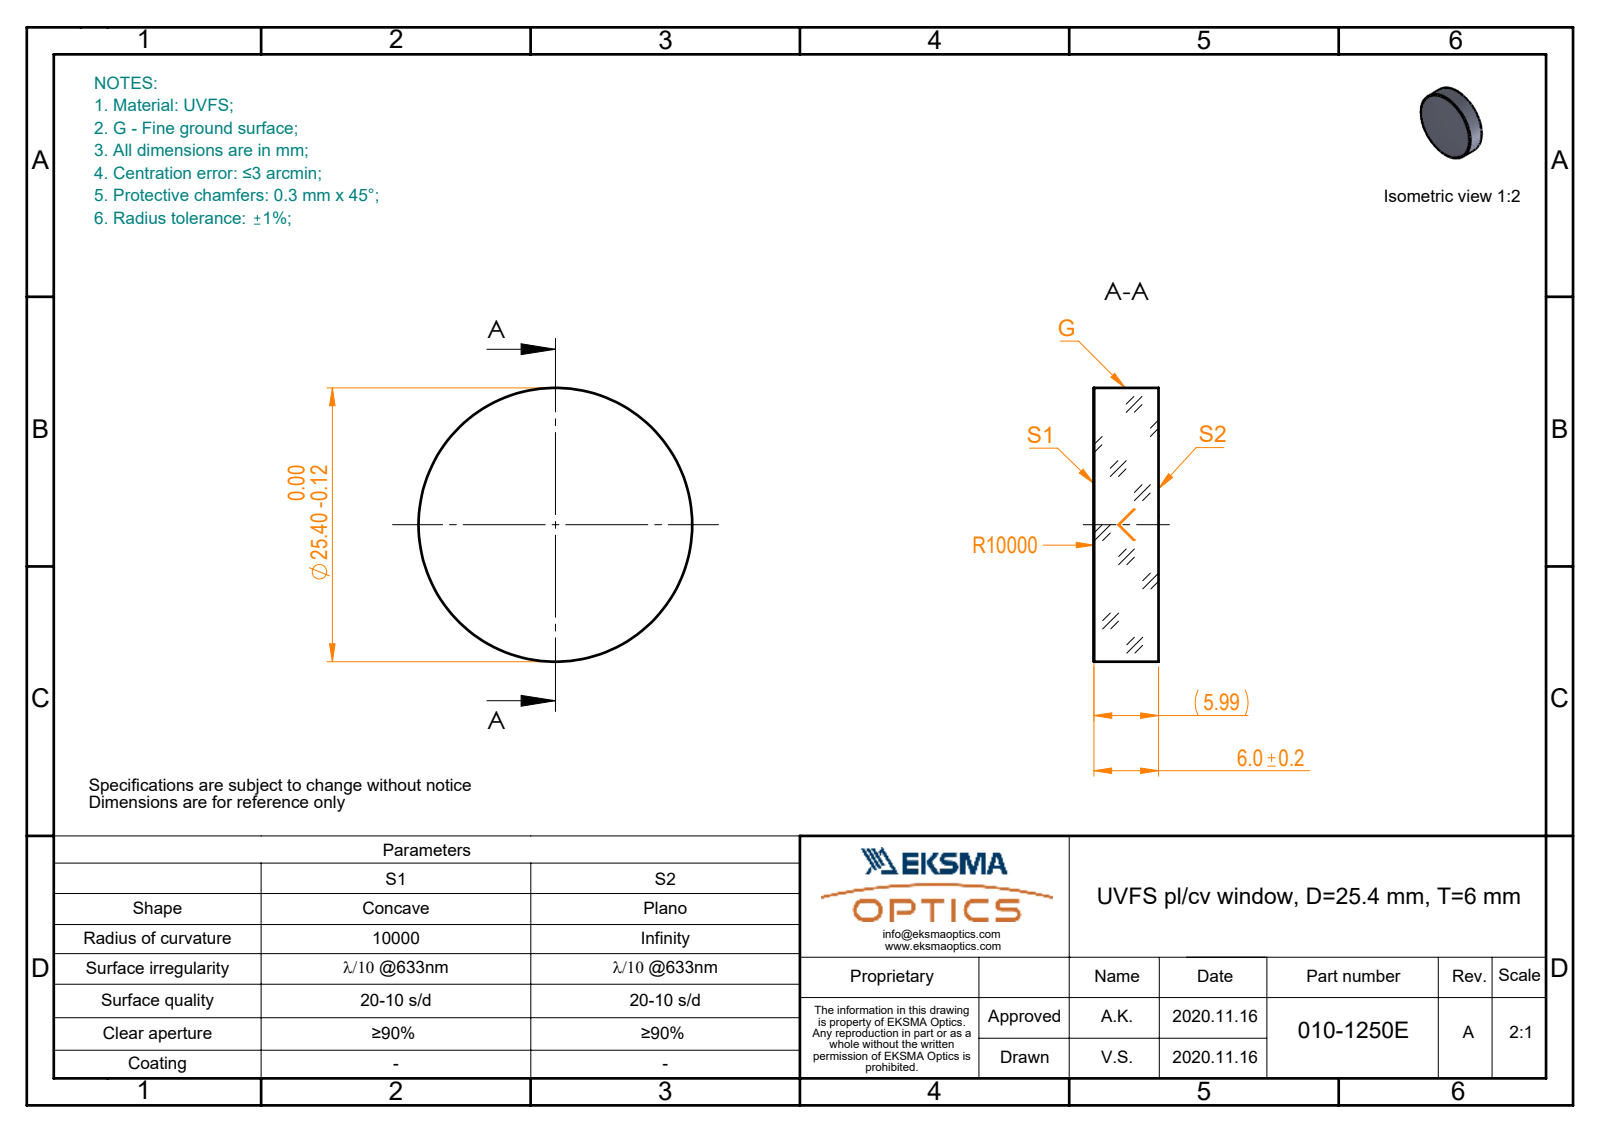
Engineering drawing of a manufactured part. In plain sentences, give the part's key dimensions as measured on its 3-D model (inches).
The part is named "010-1250E_UVFS_PCV_window". Its 3-D file was written by "SolidWorks 2019 (CONFIG_CONTROL_DESIGN)". It is 1 solid with 5 faces: 1 planar, 2 cylindrical and 2 other. Overall it measures 1 by 1 by 0.236 inches. Its volume is 0.185 cubic inches and its surface area 2.313 square inches. Round bosses or shafts: 1 of diameter 1.
